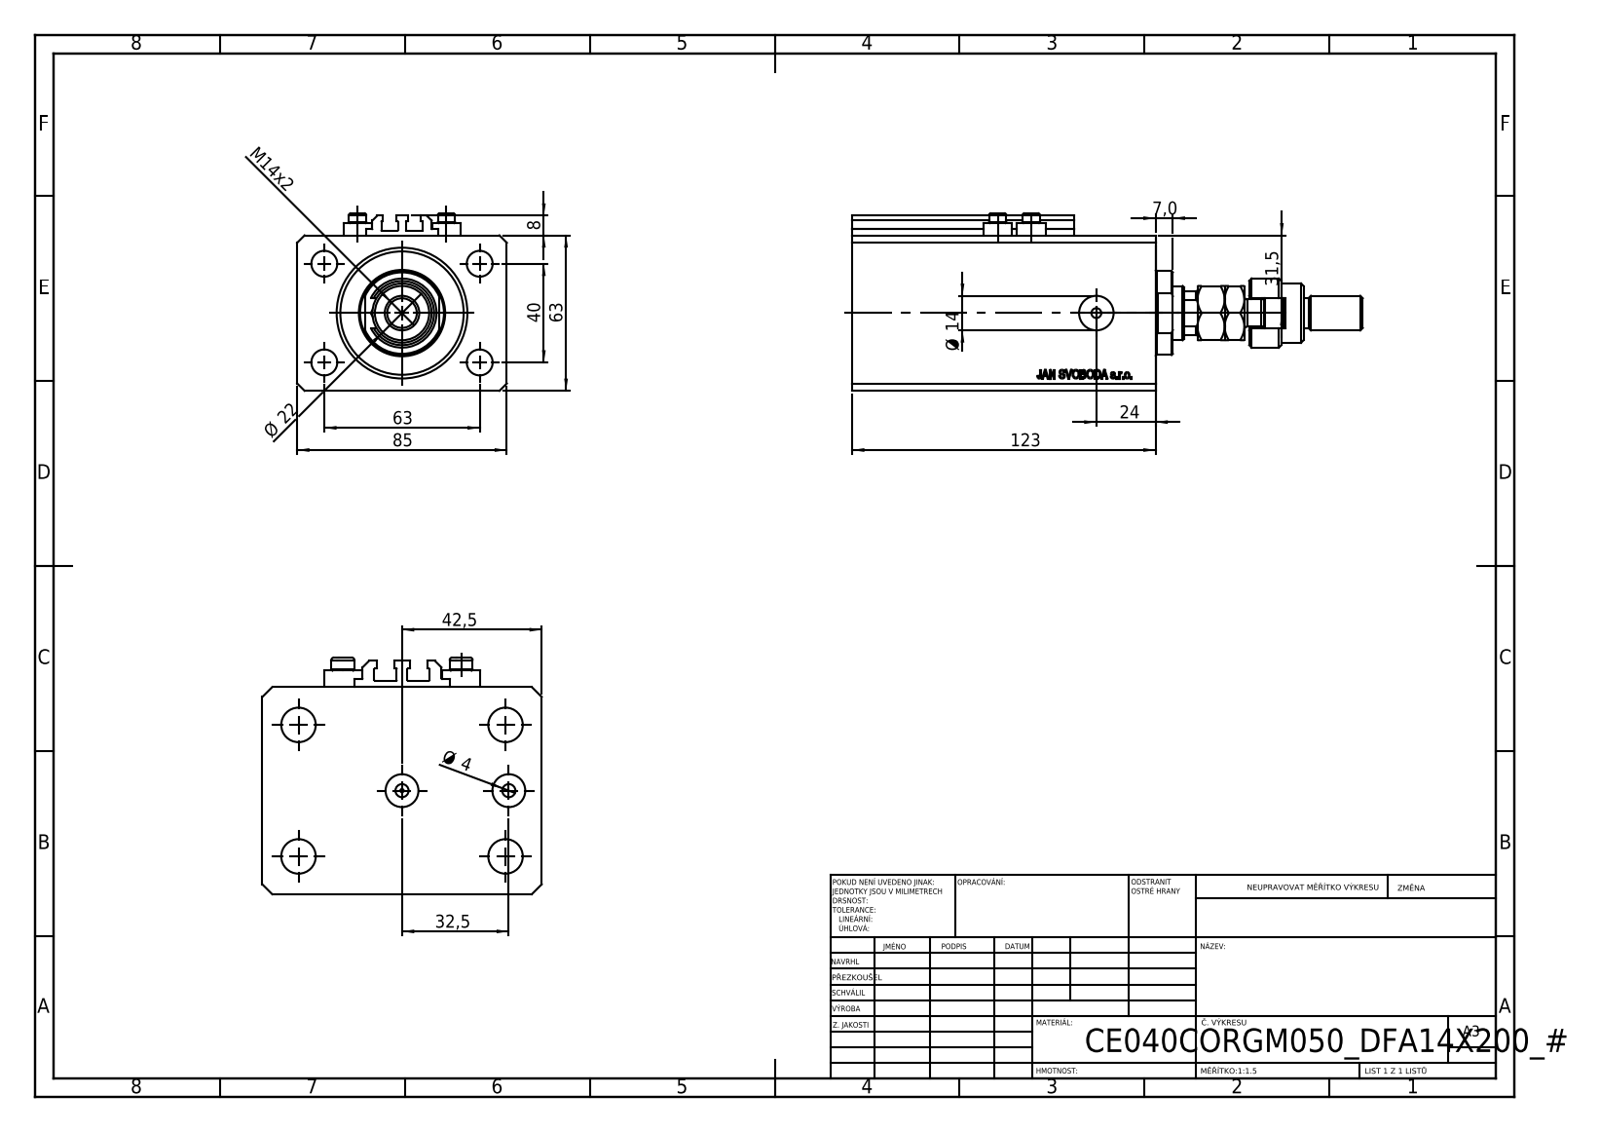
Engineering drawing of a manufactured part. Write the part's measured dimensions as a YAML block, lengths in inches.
part_name: "V250CE_C_Body; V250CE_C_VCP; V250CE_VC_C; MFA (+2 more)"
step_written_by: "SolidWorks 2019 (CONFIG_CONTROL_DESIGN)"
units: inches
bodies: {solids: 10, faces: 1123, planar: 532, cylindrical: 101, other: 490}
overall_size: [8.15, 3.346, 2.835]
volume: 37.15
surface_area: 189.3
round_holes:
  - {diameter: 0.157, count: 8}
  - {diameter: 0.413, count: 4}
  - {diameter: 0.394, count: 2}
  - {diameter: 0.551, count: 2}
  - {diameter: 0.049, count: 1}
  - {diameter: 0.492, count: 1}
  - {diameter: 0.866, count: 1}
  - {diameter: 1.575, count: 1}
  - {diameter: 2.087, count: 1}
round_bosses_or_shafts:
  - {diameter: 0.457, count: 4}
  - {diameter: 0.276, count: 4}
  - {diameter: 1.339, count: 1}
  - {diameter: 1.102, count: 1}
  - {diameter: 0.945, count: 1}
  - {diameter: 0.709, count: 1}
  - {diameter: 0.551, count: 1}
  - {diameter: 0.472, count: 1}
partial_cylinders:
  - {radius: 0.008, count: 10}
  - {radius: 0.384, count: 1}
  - {radius: 0.413, count: 1}
face_to_face_distances: [2.48, 3.346, 4.843, 0.669, 4.173, 0.449, 3.724, 4.394, 0.394, 0.079]
hole_center_spacings: [1.469, 0.535, 0.788, 1.417, 1.515, 1.575, 2.48, 2.64]
